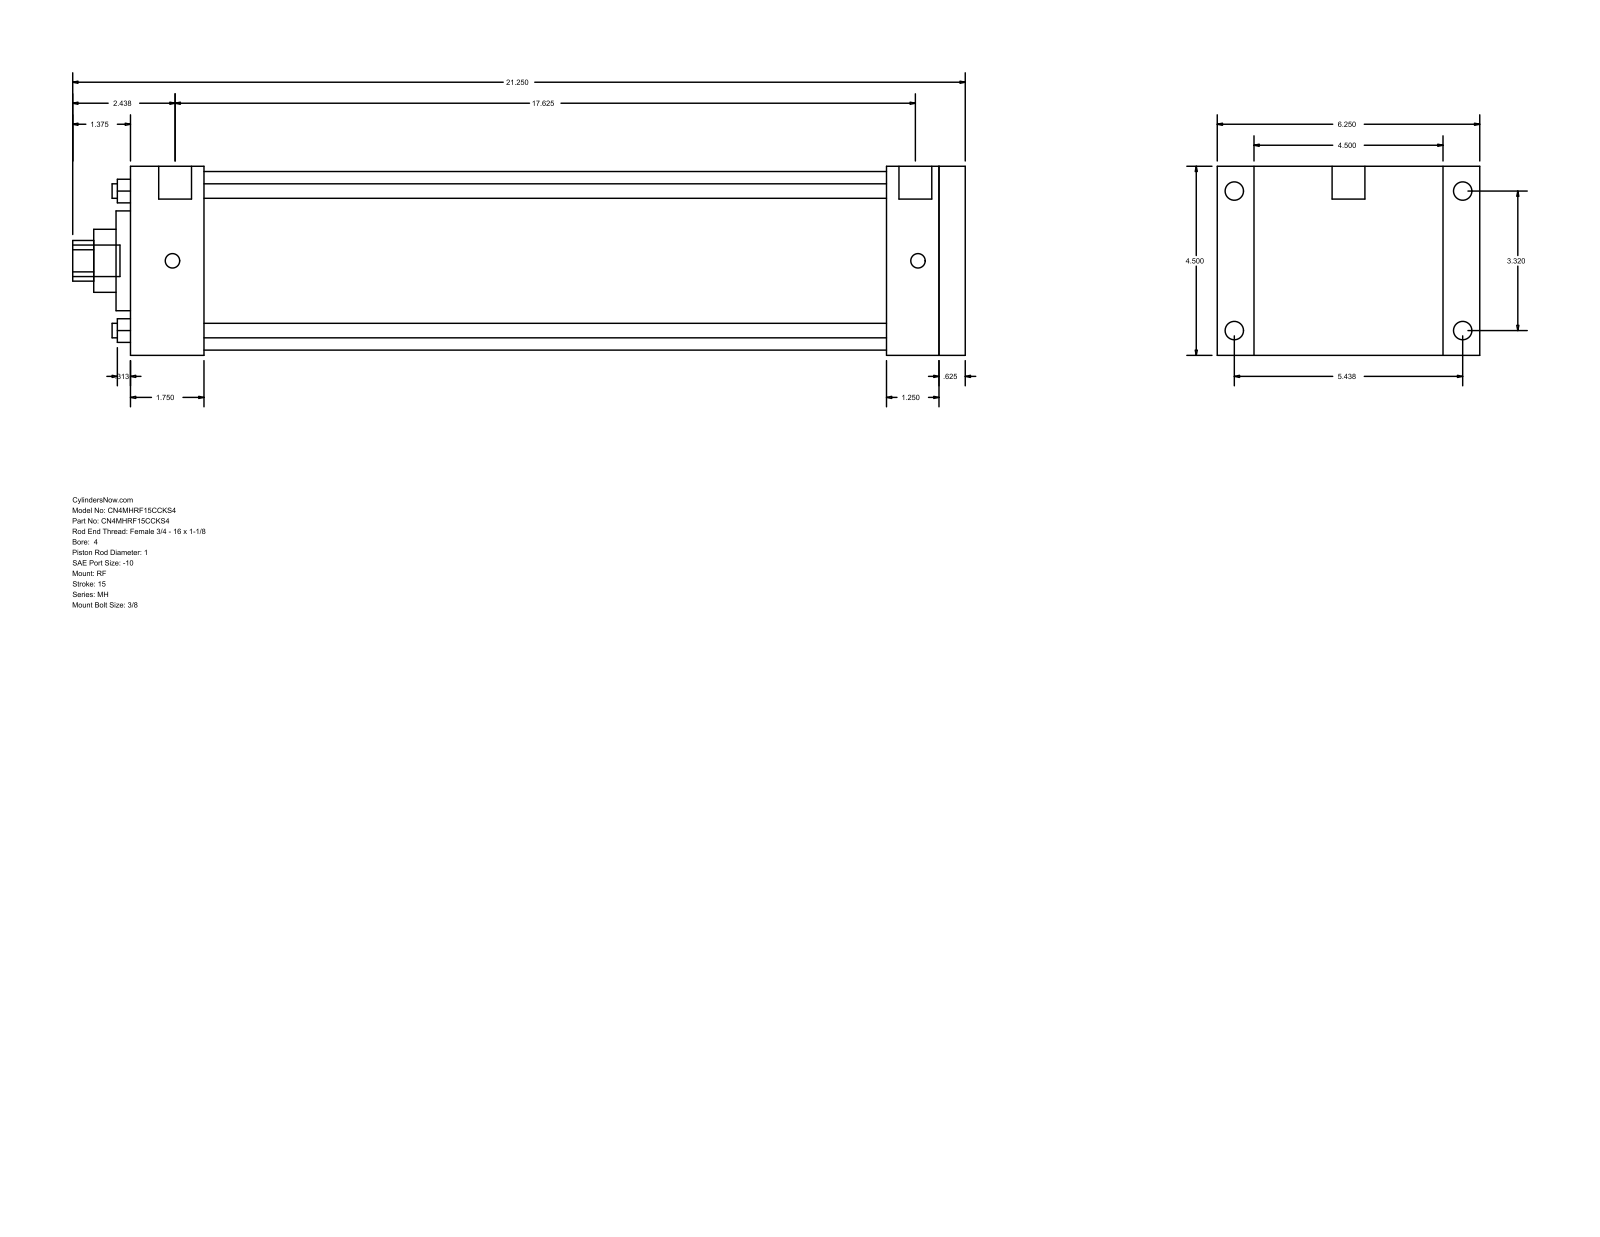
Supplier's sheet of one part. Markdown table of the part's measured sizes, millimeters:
| quantity | value |
| --- | --- |
| part name | MH_RF__0400_1 |
| STEP written by | GSSL Pune (CONFIG_CONTROL_DESIGN) |
| units | millimeters |
| bodies | 0 solids, 94 faces (65 planar, 29 cylindrical, 0 other) |
| overall size | 539.75 × 158.75 × 114.3 |
| round holes (diameter × count) | 8.76 × 4, 25.4 × 1, 38.1 × 1, 60.33 × 1, 107.95 × 1 |
| round bosses / shafts (diameter × count) | 11.13 × 4, 8.73 × 4, 19.84 × 2, 19.05 × 1 |
| partial cylindrical surfaces (radius × count) | 12.29 × 1 |
| main face-to-face distances | 114.3, 504.83, 15.87, 488.96, 47.63, 44.46, 444.5, 460.37, 457.2, 412.74 |
| hole center spacings | 59.62, 84.32, 119.25 |
